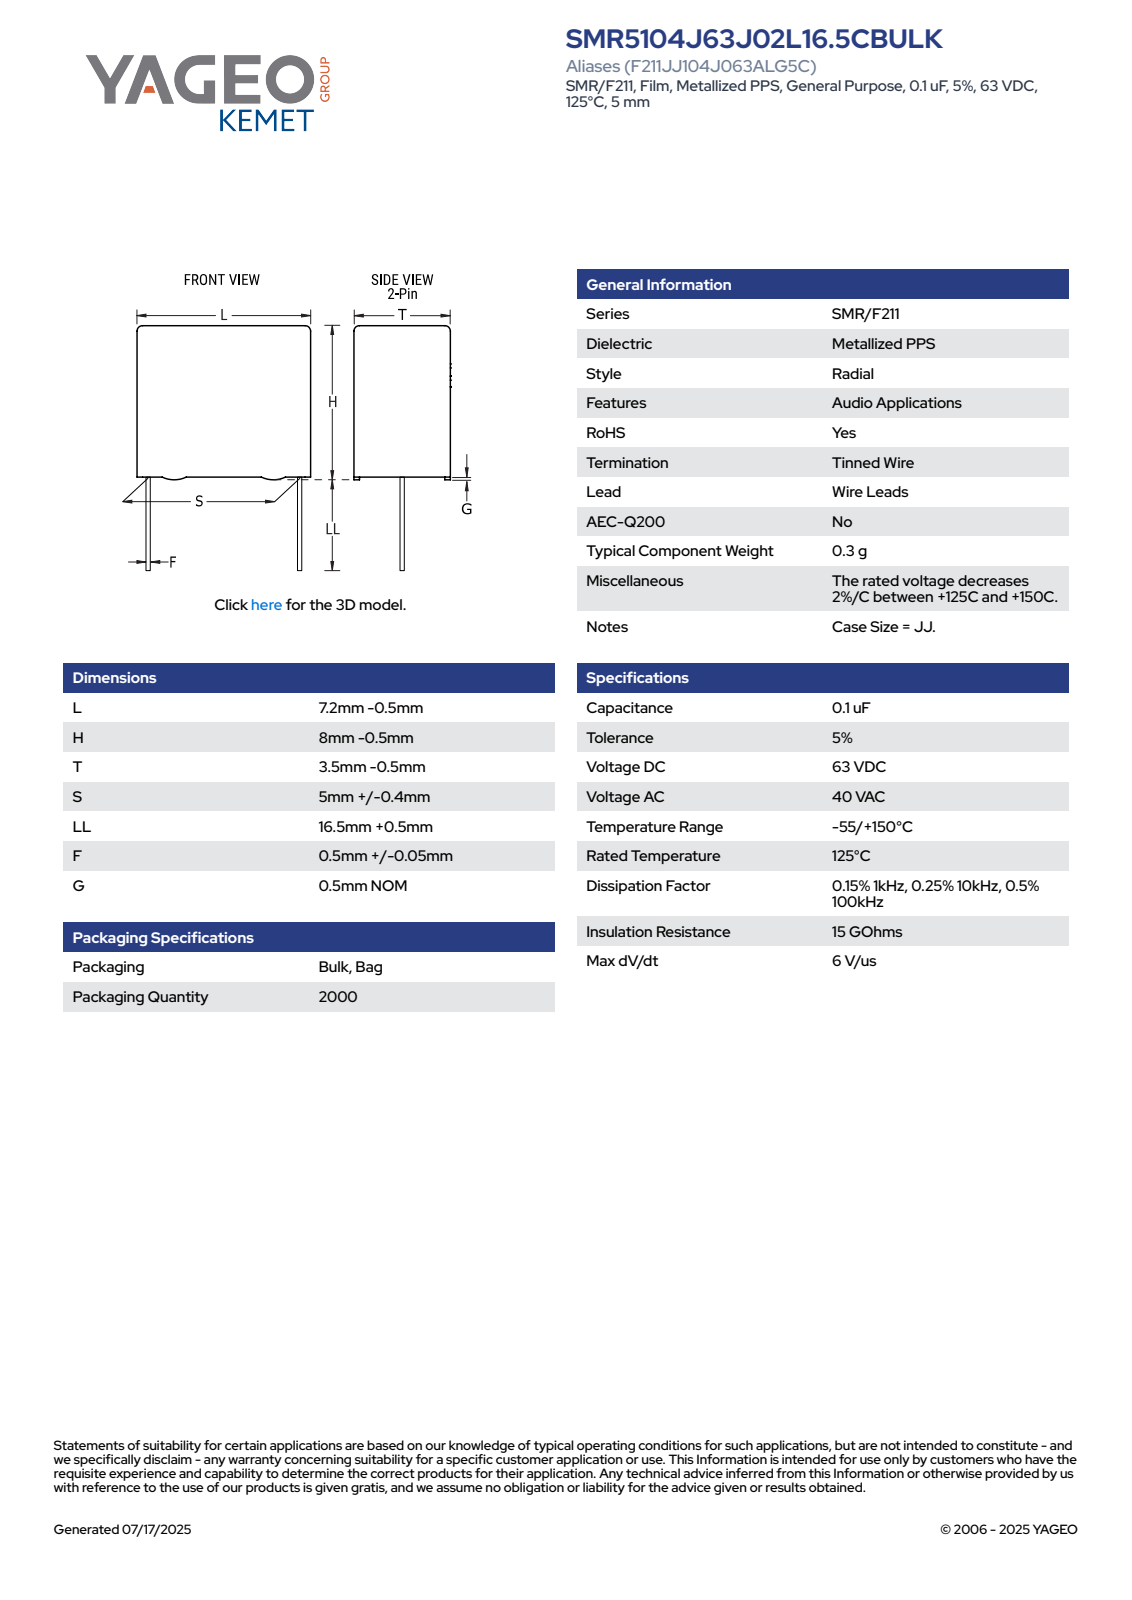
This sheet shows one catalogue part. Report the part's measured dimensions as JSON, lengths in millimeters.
{"part_name": "CFR_RBG_7.2X8X3.5_L6.7H7.5T3S5LL17F0.55G0.5", "step_written_by": "SolidWorks 2021 (AUTOMOTIVE_DESIGN)", "units": "millimeters", "bodies": {"solids": 4, "faces": 89, "planar": 81, "cylindrical": 8, "other": 0}, "overall_size": [24.5, 6.7, 3], "volume_mm3": 148, "surface_area_mm2": 242, "round_bosses_or_shafts": [[0.55, 2]], "partial_cylinders_radius": [[0.5, 4]], "face_to_face_distances": [3, 6.7, 7, 2.83, 2.66, 0.5, 7.5, 17, 17.5, 24.5]}
